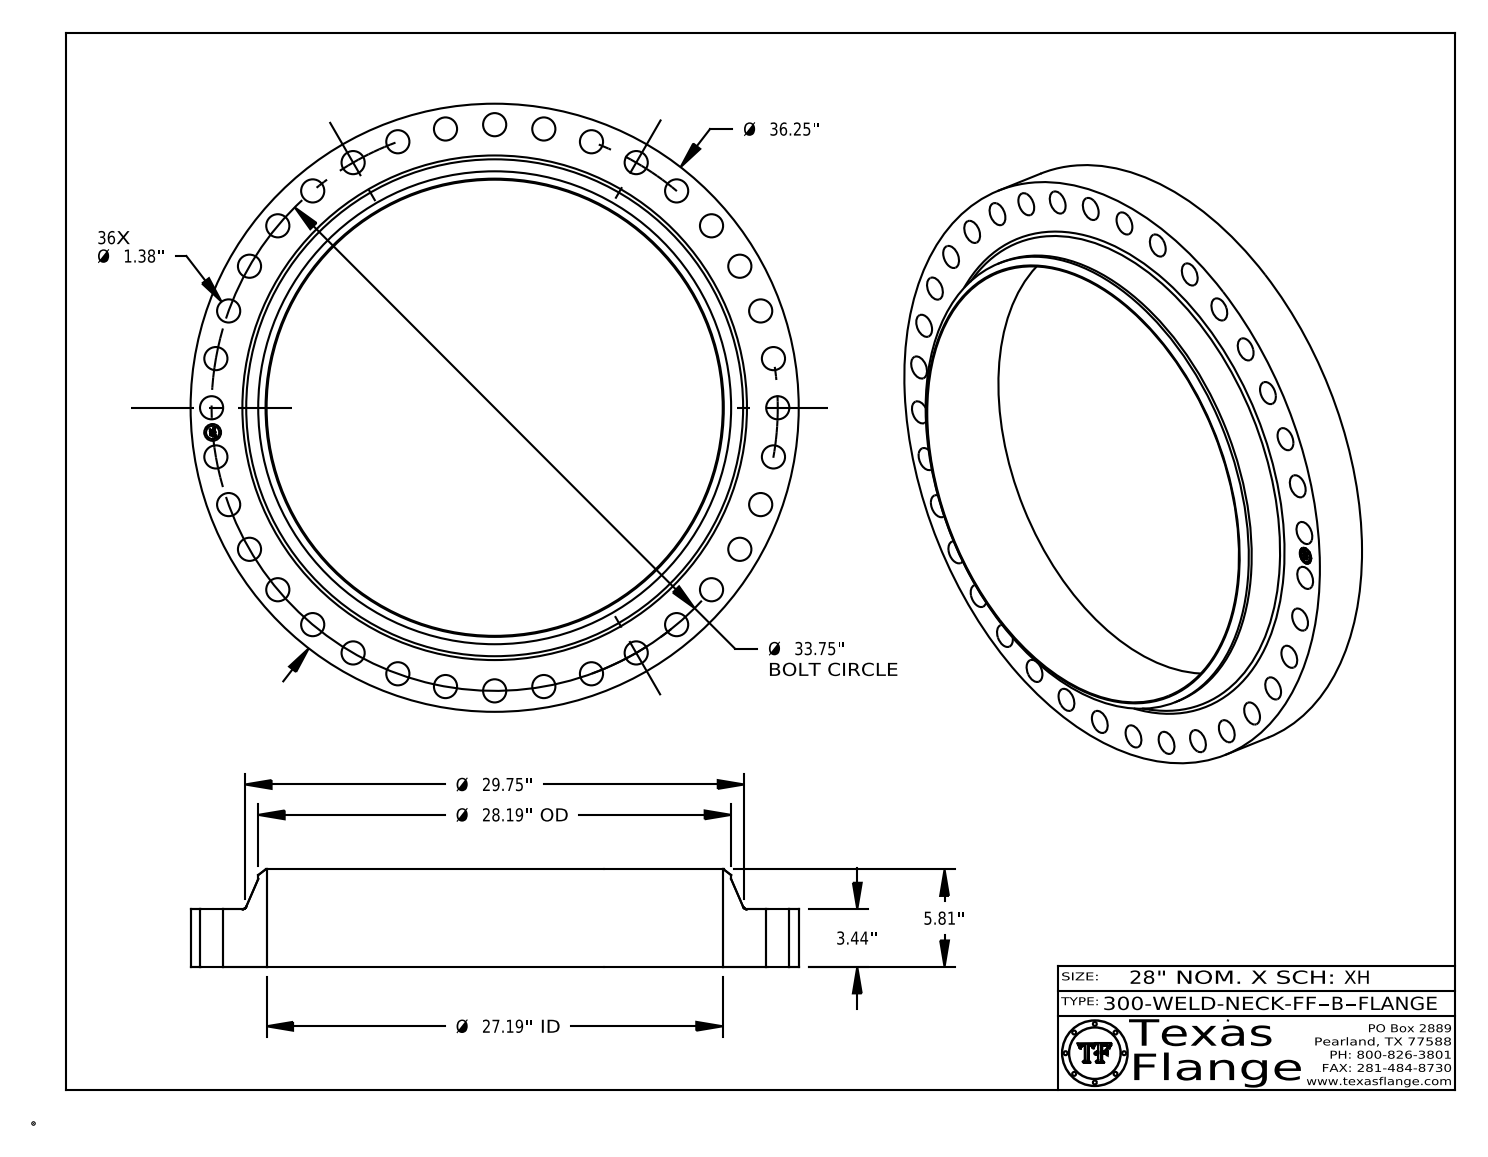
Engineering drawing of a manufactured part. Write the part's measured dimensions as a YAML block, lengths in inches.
part_name: "300-WELD-NECK-FF, Series B"
step_written_by: "CATIA V5 STEP AP214 (AUTOMOTIVE_DESIGN)"
units: inches
bodies: {solids: 1, faces: 472, planar: 368, cylindrical: 98, other: 6}
overall_size: [36.25, 36.25, 5.81]
volume: 1528
surface_area: 2355
round_holes:
  - {diameter: 1.38, count: 36}
  - {diameter: 1, count: 1}
  - {diameter: 27.19, count: 1}
round_bosses_or_shafts:
  - {diameter: 0.061, count: 8}
  - {diameter: 36.25, count: 1}
  - {diameter: 28.19, count: 1}
  - {diameter: 0.788, count: 1}
face_to_face_distances: [3.44, 5.81, 2.37, 0.015, 3.425, 2.385, 0.298, 0.292, 0.054, 0.193]
hole_center_spacings: [16.875, 33.622, 32.6, 16.875, 23.865, 2.941, 21.694, 25.854]
